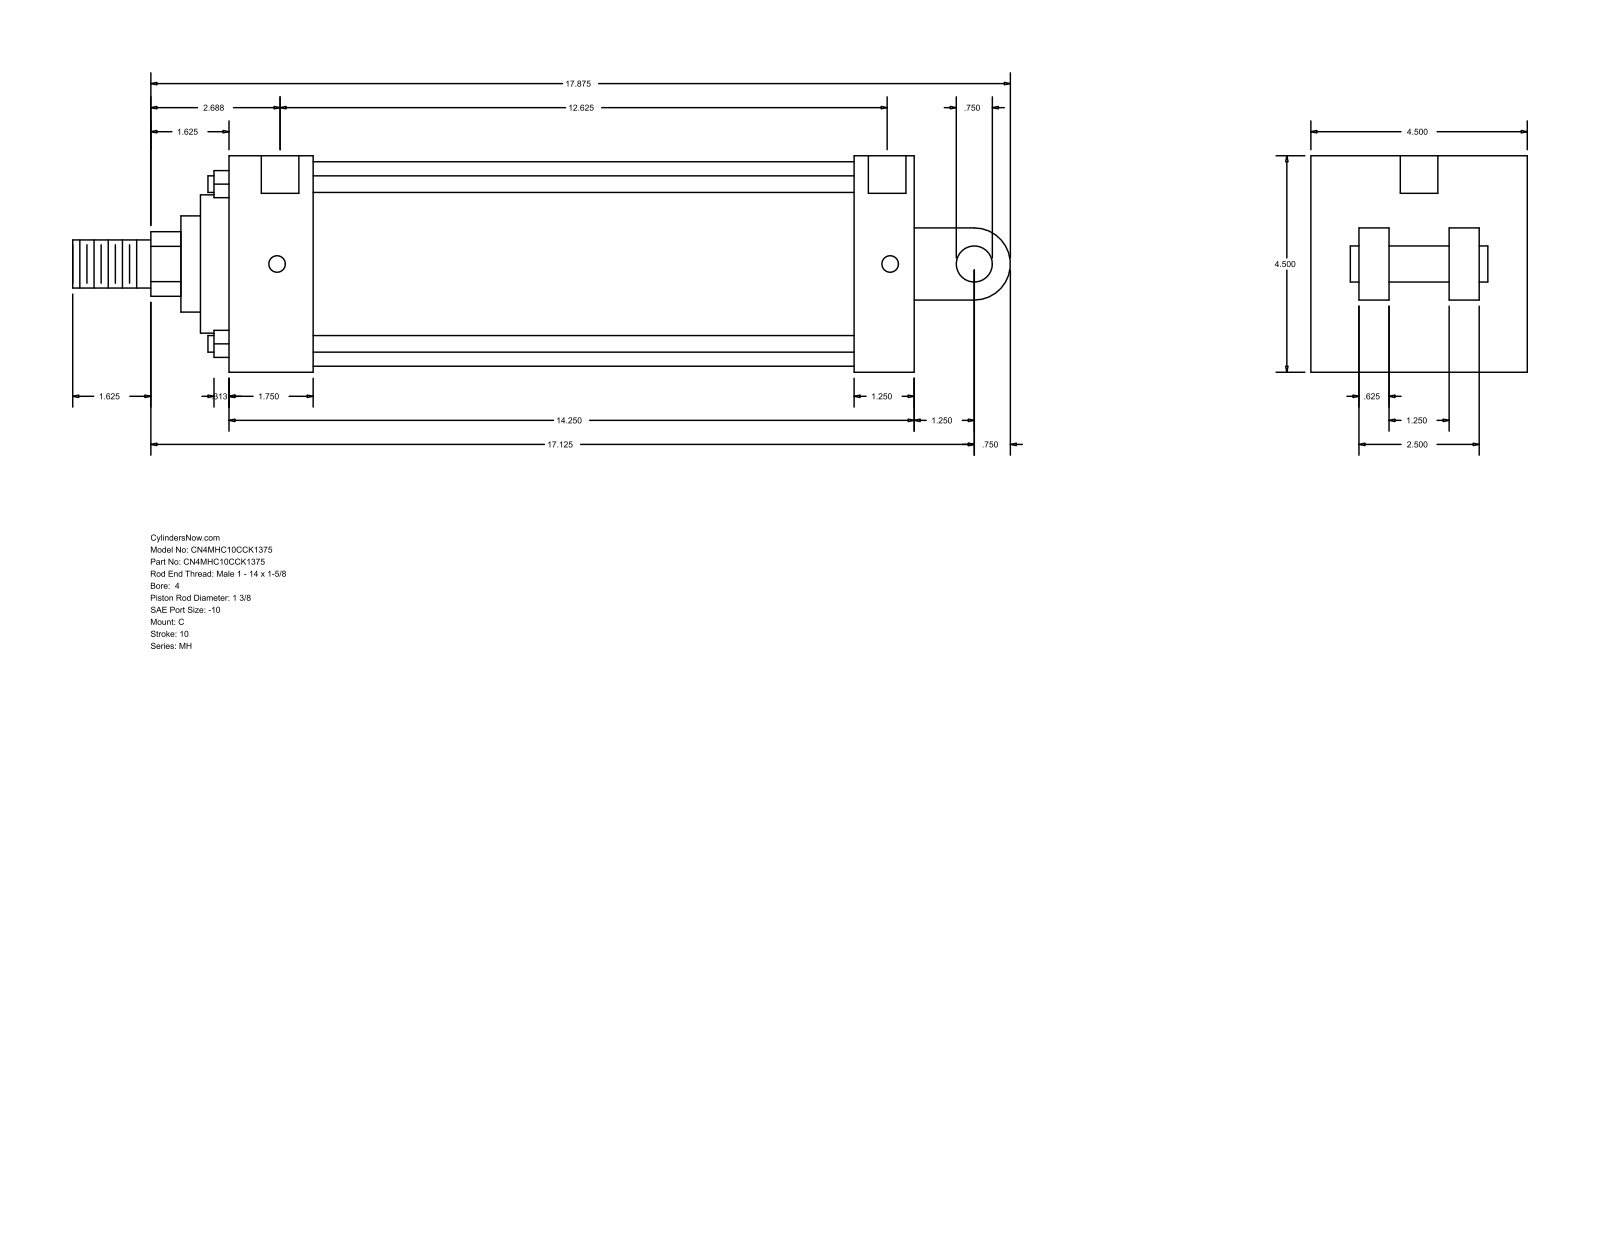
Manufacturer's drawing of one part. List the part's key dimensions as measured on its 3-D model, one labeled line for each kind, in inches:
Part name (STEP PRODUCT): MH_C__0400_1.375
STEP written by: GSSL Pune (CONFIG_CONTROL_DESIGN)
Units: inches
Bodies: 0 solids, 101 faces (71 planar, 30 cylindrical, 0 other)
Overall size (bounding box): 19.5 × 4.5 × 4.5
Round holes (diameter × count): ⌀0.344 ×4, ⌀0.781 ×2
Round bosses / shafts (diameter × count): ⌀0.345 ×4, ⌀4.25 ×1, ⌀2.875 ×1, ⌀2 ×1, ⌀1.375 ×1, ⌀1 ×1, ⌀0.75 ×1
Partial cylindrical surfaces — rounded edges, fillets, slot ends (radius × count): R0.672 ×1, R0.75 ×1
Main face-to-face distances: 4.5, 14.25, 1.75, 13, 11.25, 12.5, 1.25, 1.625, 2.875, 1.5
Hole centre spacings: 12.75, 0.062, 0.063, 12.625, 12.687, 12.688
